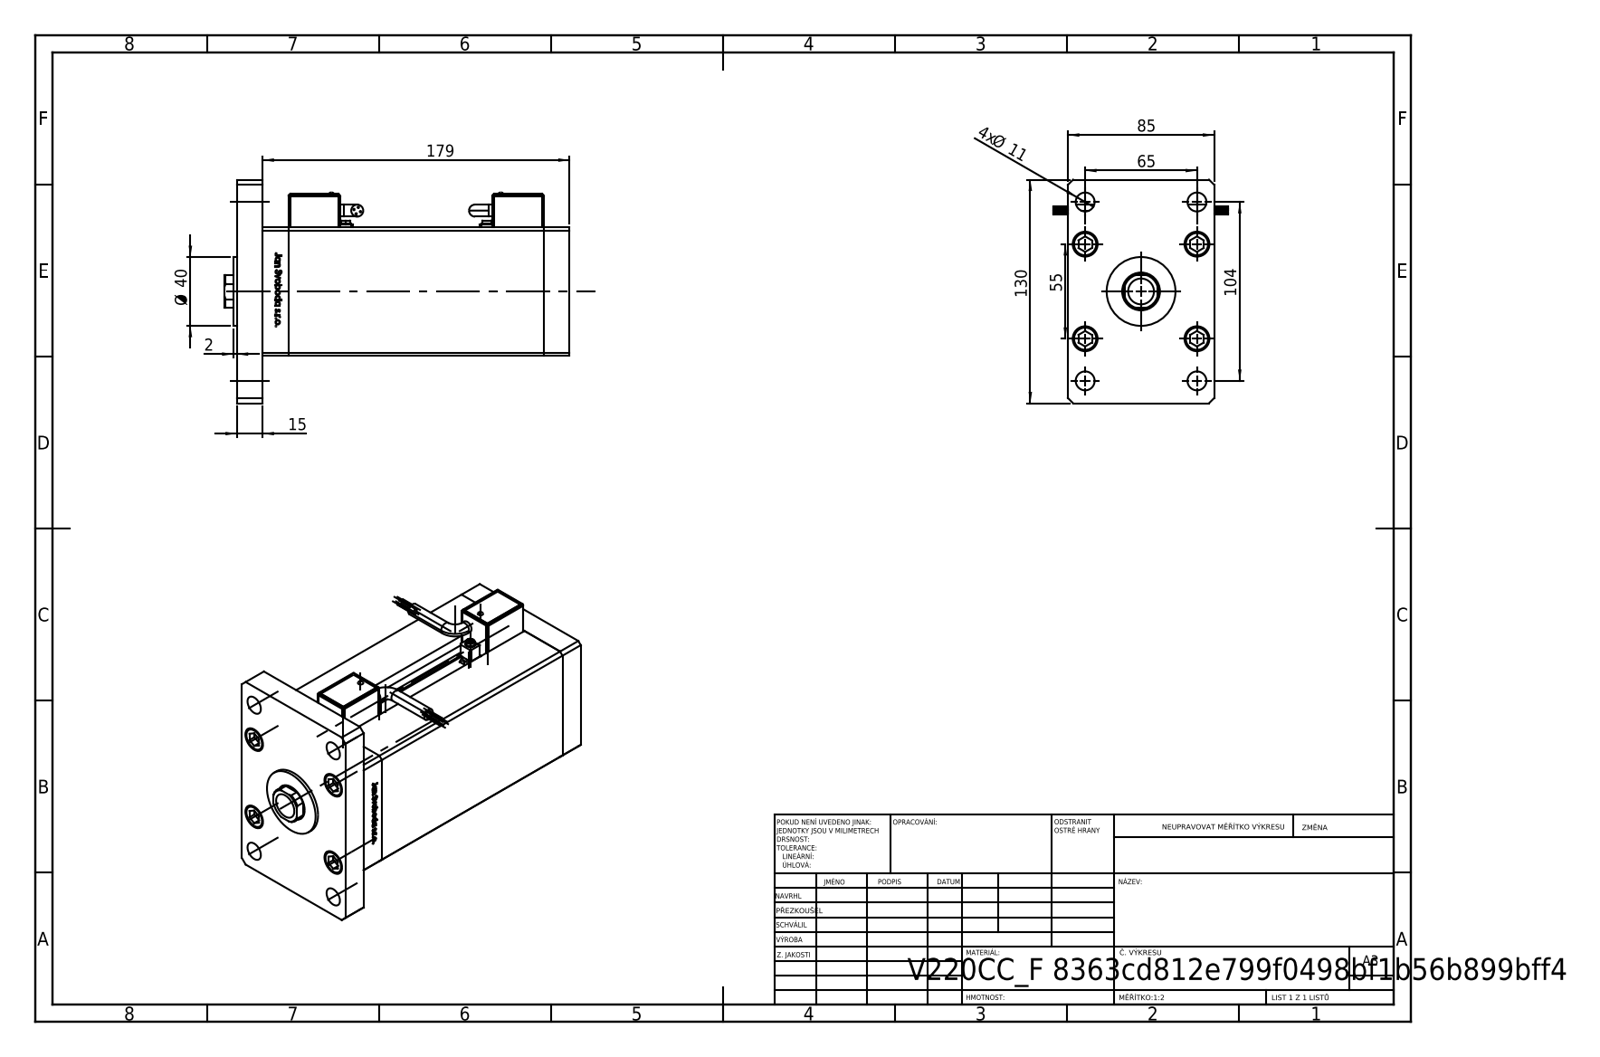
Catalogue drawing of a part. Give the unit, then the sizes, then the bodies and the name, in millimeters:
Units: millimetres
Overall size (bounding box): 200.5 × 130 × 101.6
Round holes (diameter × count): ⌀11 ×9, ⌀15.5 ×5, ⌀10 ×4, ⌀14.5 ×4, ⌀2 ×2, ⌀3.6 ×2, ⌀5 ×2, ⌀7 ×2, ⌀13.16 ×2, ⌀15 ×1, ⌀22 ×1, ⌀38 ×1
Round bosses / shafts (diameter × count): ⌀8 ×9, ⌀0.85 ×8, ⌀14.5 ×5, ⌀7 ×4, ⌀6 ×2, ⌀3.5 ×2, ⌀2.5 ×2, ⌀40 ×1
Partial cylindrical surfaces — rounded edges, fillets, slot ends (radius × count): R1 ×24, R4 ×4, R0.93 ×2, R10.5 ×1
Main face-to-face distances: 15, 163.5, 85, 178.5, 75, 148.5, 30, 193.5, 10.5, 68.5
Hole centre spacings: 28, 24.5, 42.57, 61.32, 65, 69.46, 79.5, 102.69
Volume: 1 200 000 mm³ · Surface area: 207 936 mm²
Bodies: 21 solids, 1506 faces (593 planar, 273 cylindrical, 640 other)
Part name (STEP PRODUCT): ALLEN BOLT; V220C_F_VC; Magnetic_Switch_MSU4; V220C_F (+3 more)
STEP written by: SolidWorks 2019 (CONFIG_CONTROL_DESIGN)
